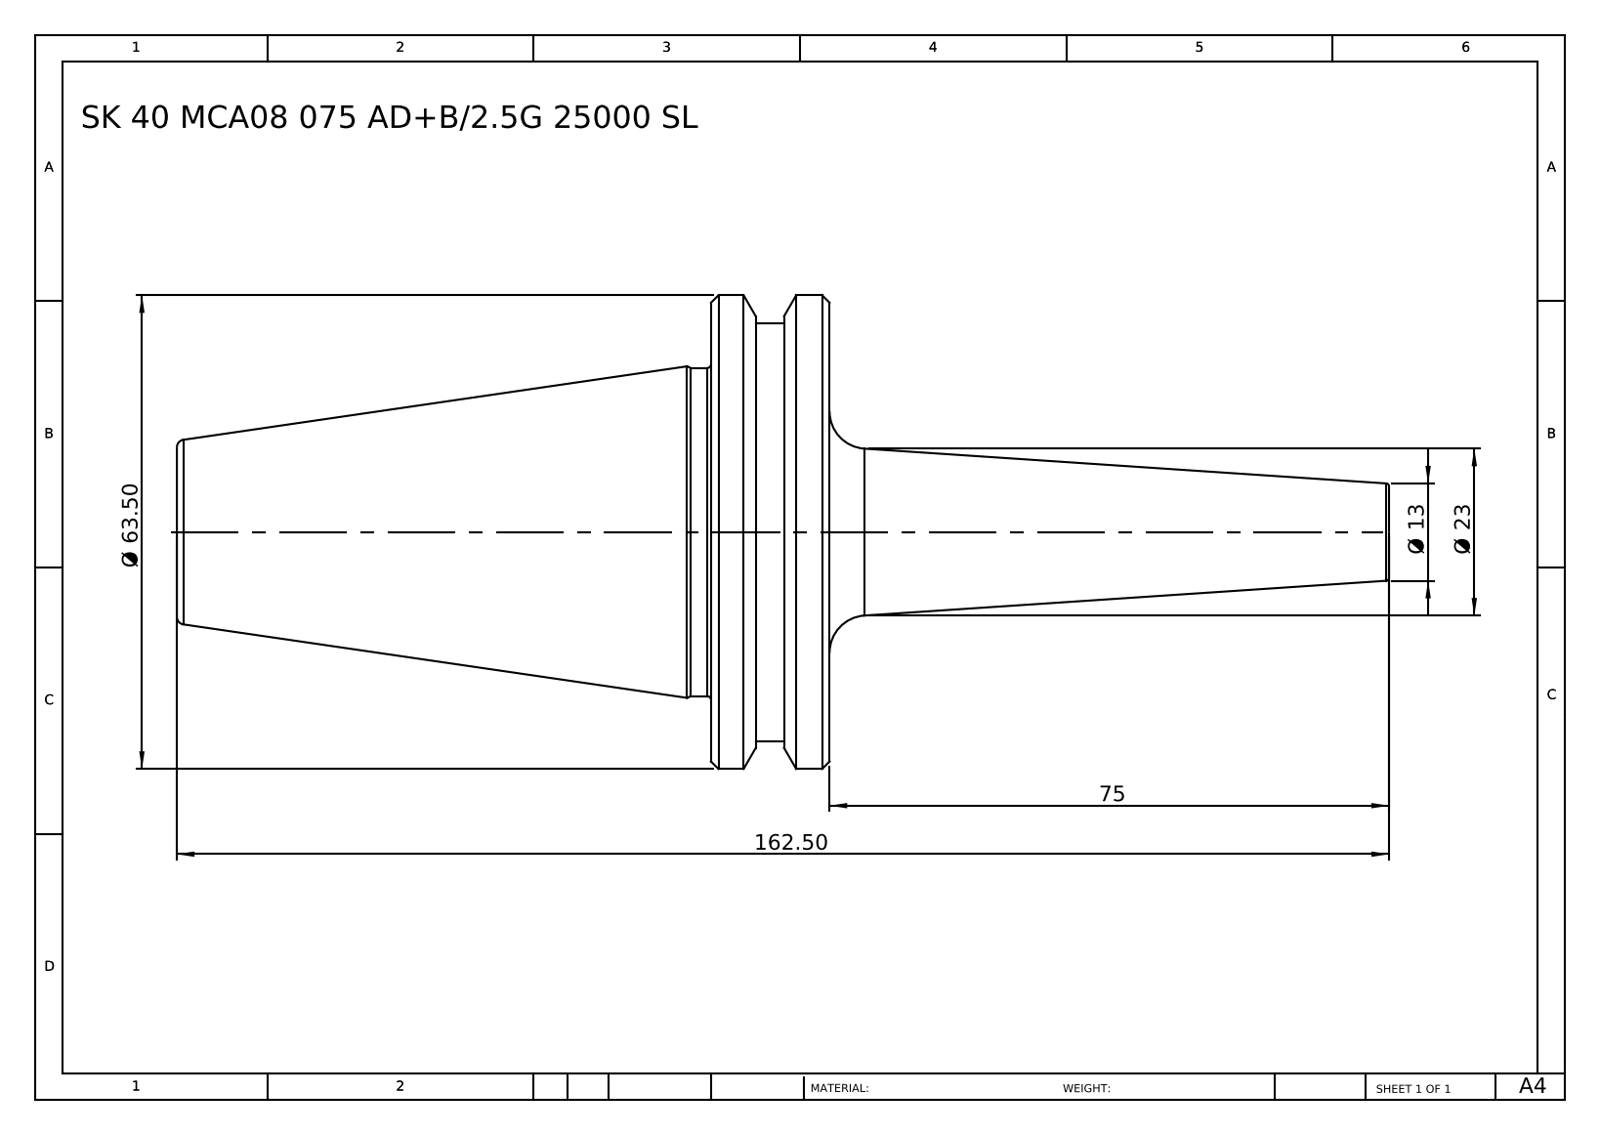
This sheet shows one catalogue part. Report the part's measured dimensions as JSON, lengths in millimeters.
{"part_name": "SK 40 MCA08 075 AD+B-2.5G 25000 SL", "step_written_by": "SolidWorks 2014 (CONFIG_CONTROL_DESIGN)", "units": "millimeters", "bodies": {"solids": 1, "faces": 36, "planar": 6, "cylindrical": 8, "other": 22}, "overall_size": [162.5, 63.5, 63.5], "volume_mm3": 137040, "surface_area_mm2": 20781, "round_bosses_or_shafts": [[63.5, 1], [56, 1], [44, 1]], "face_to_face_distances": [15.9, 87.5, 71.6, 6.1, 9.8, 81.4, 9.9, 3.8, 6, 77.6]}
